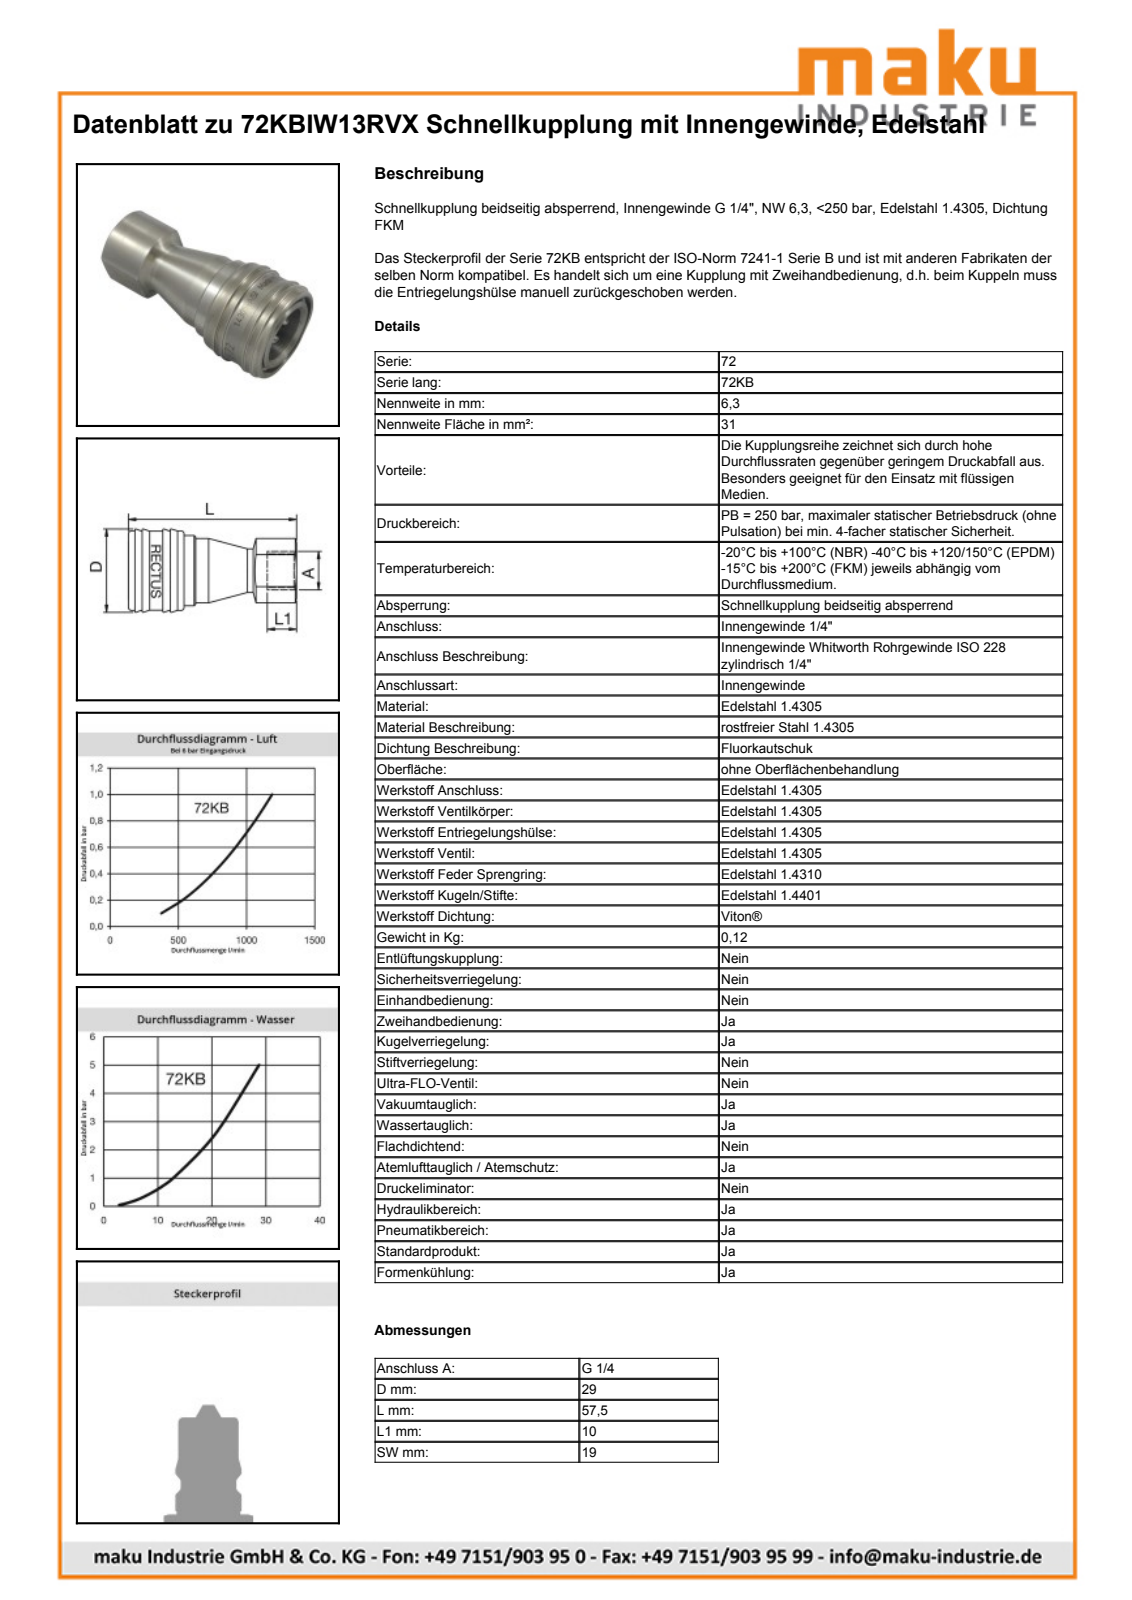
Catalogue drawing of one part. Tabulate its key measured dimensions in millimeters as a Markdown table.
| quantity | value |
| --- | --- |
| part name | D110472 |
| STEP written by | Autodesk Inventor 2013 (AUTOMOTIVE_DESIGN) |
| units | millimeters |
| bodies | 3 solids, 621 faces (186 planar, 76 cylindrical, 359 other) |
| overall size | 57.5 × 28.5 × 28.5 |
| volume | 20 656 mm³ |
| surface area | 9 197 mm² |
| round holes (diameter × count) | 11.45 × 1, 21.15 × 1, 23.8 × 1, 24.5 × 1 |
| round bosses / shafts (diameter × count) | 27.15 × 1, 27 × 1, 24 × 1, 22 × 1, 20.9 × 1, 14.9 × 1 |
| partial cylindrical surfaces (radius × count) | 9.07 × 1, 13.4 × 1 |
| main face-to-face distances | 19, 57.5, 6.7, 50.8, 44.5, 37.8, 13, 17.5, 10.8, 27 |
